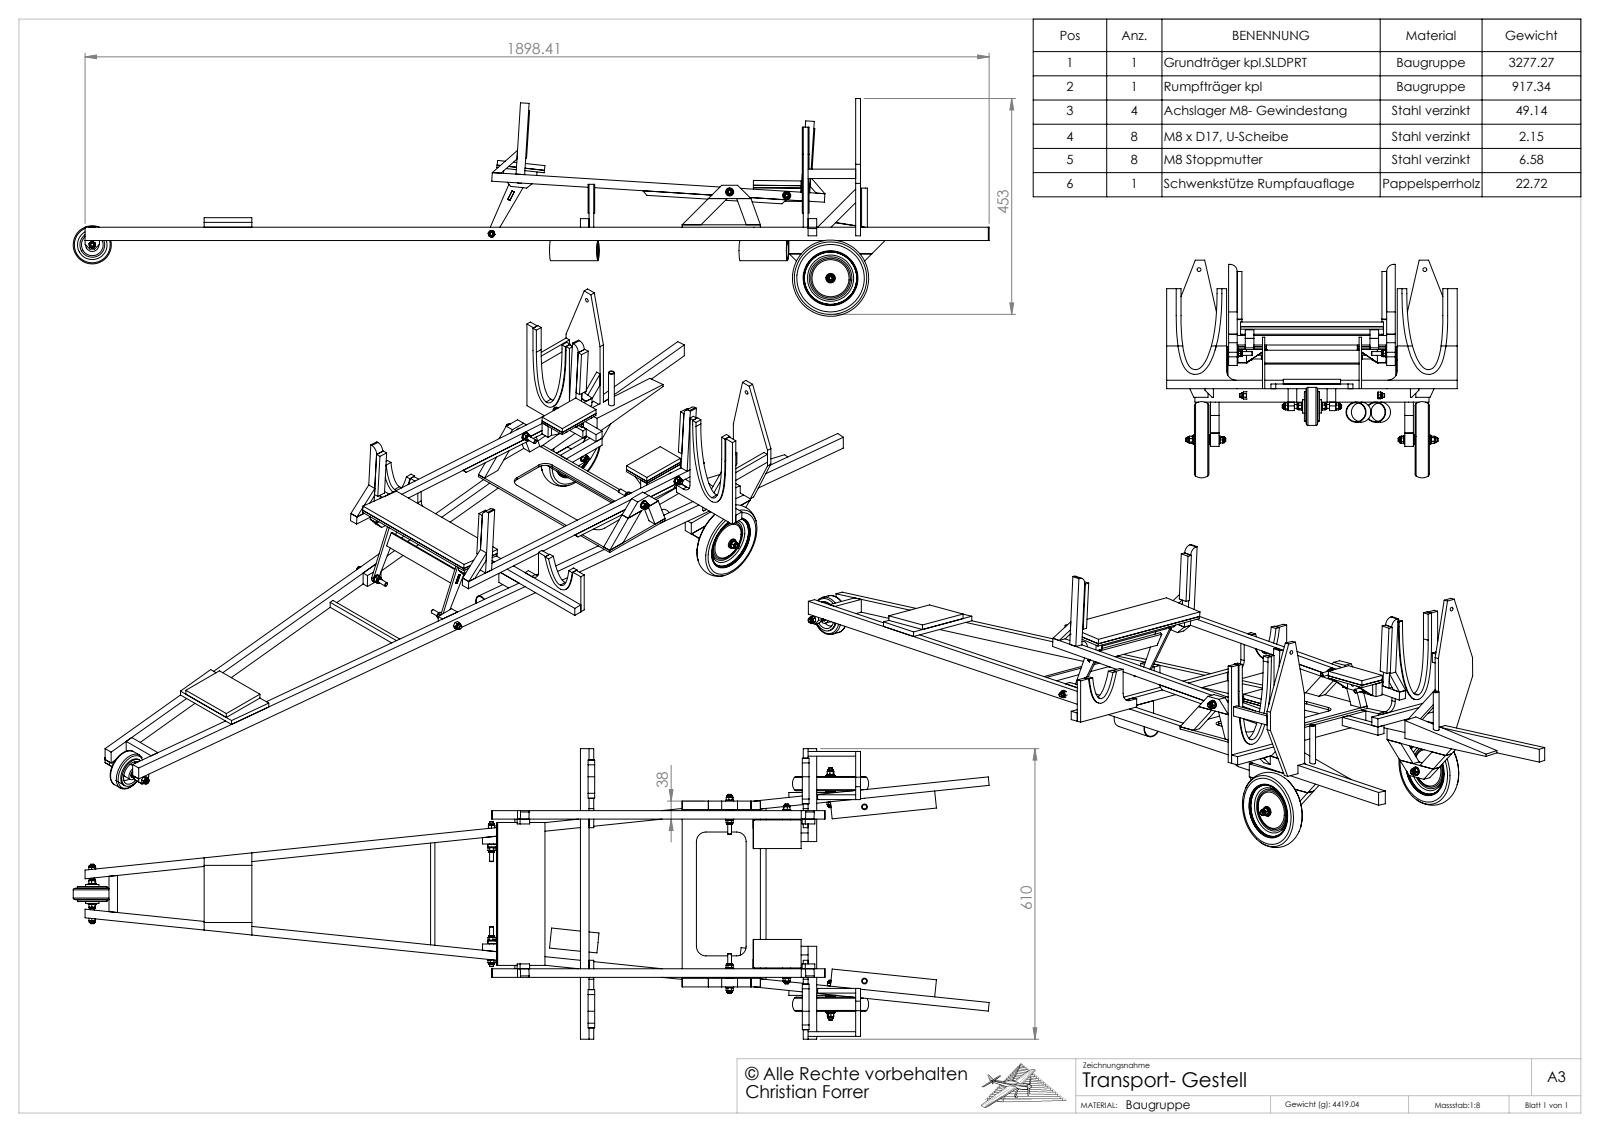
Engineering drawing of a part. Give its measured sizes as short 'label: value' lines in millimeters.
name: M8 x D17, U-Scheibe; M8 Stoppmutter; Achslager M8- Gewindestang; Schwenkstütze Rumpfauaflage (+8 more)
written by: SolidWorks 2010 (CONFIG_CONTROL_DESIGN)
unit: mm
bodies: 145 solids, 1494 faces (830 planar, 316 cylindrical, 348 other)
size: 1923.41 × 610 × 457
volume: 7 416 000 mm³; area: 1 992 000 mm²
holes: 8× ⌀8, 5× ⌀8.4, 2× ⌀9, 2× ⌀12, 2× ⌀40, 1× ⌀12.2, 1× ⌀12.3, 1× ⌀20, 1× ⌀78
bosses: 5× ⌀17, 5× ⌀12.5, 2× ⌀42.2, 2× ⌀12, 1× ⌀110, 1× ⌀80, 1× ⌀62, 1× ⌀27.8
rounds: 6× R20, 4× R15, 1× R8
face distances: 18, 10, 28, 5, 18.44, 38, 20, 110, 370, 15
hole spacings: 39.99, 80.1, 120, 130, 196.41, 218.34, 278.72, 365.56
